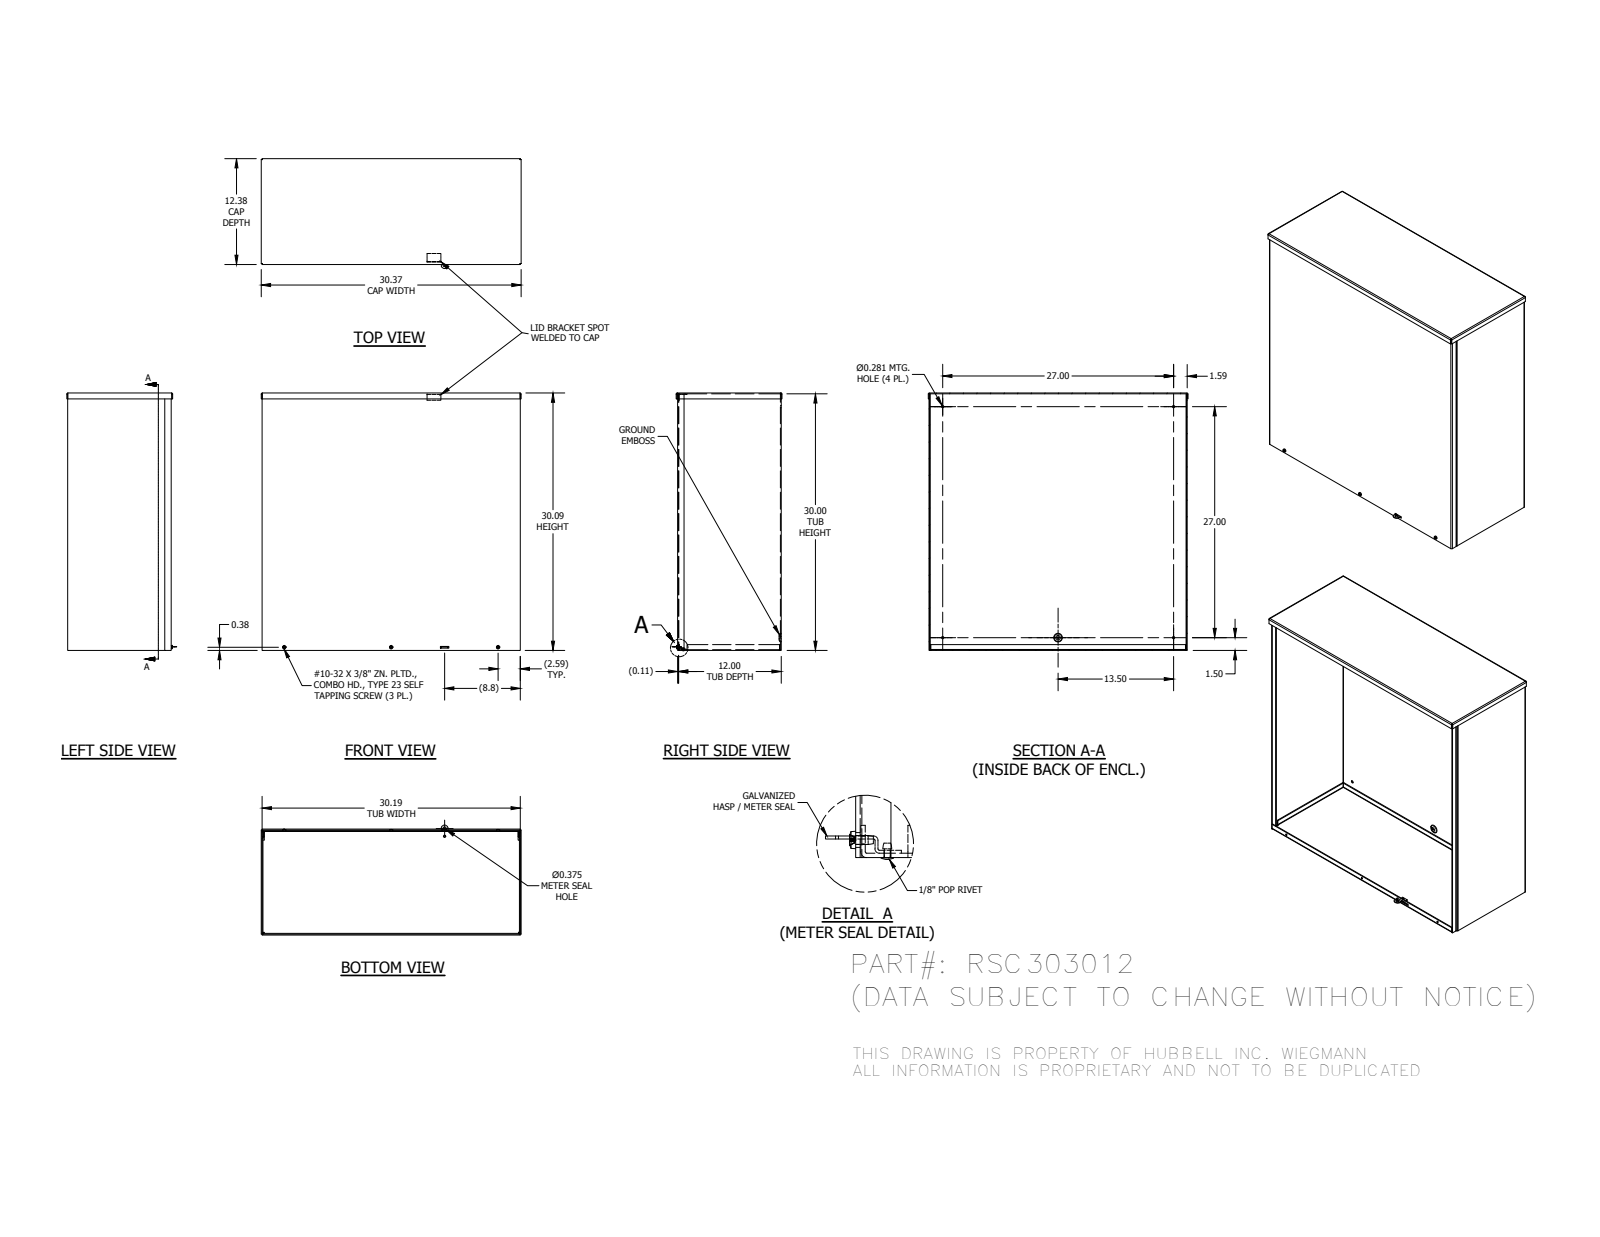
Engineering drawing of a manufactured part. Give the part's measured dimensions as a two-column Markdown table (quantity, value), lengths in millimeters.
| quantity | value |
| --- | --- |
| part name | RSC303012BKPA; RSC3012EWPA; RSC3030LFA; RSC3012CPA (+5 more) |
| STEP written by | Autodesk Inventor 2014 (AUTOMOTIVE_DESIGN) |
| units | millimeters |
| bodies | 11 solids, 367 faces (226 planar, 64 cylindrical, 77 other) |
| overall size | 771.52 × 765.4 × 326.24 |
| volume | 5 210 000 mm³ |
| surface area | 4 411 000 mm² |
| round holes (diameter × count) | 7.94 × 6, 4.34 × 4, 7.14 × 4, 3.17 × 1, 3.45 × 1, 9.52 × 1 |
| round bosses / shafts (diameter × count) | 4.83 × 3, 6.65 × 1, 3.17 × 1 |
| partial cylindrical surfaces (radius × count) | 0.79 × 19, 3.17 × 16, 2.37 × 2, 2.67 × 1, 10.16 × 1 |
| main face-to-face distances | 2.38, 305.2, 764.38, 762, 307.58, 302.82, 766.76, 759.62, 3.79, 760.59 |
| hole center spacings | 317.5, 344.09, 661.02, 685.8, 807.95, 742.95, 38.23, 38.24 |
